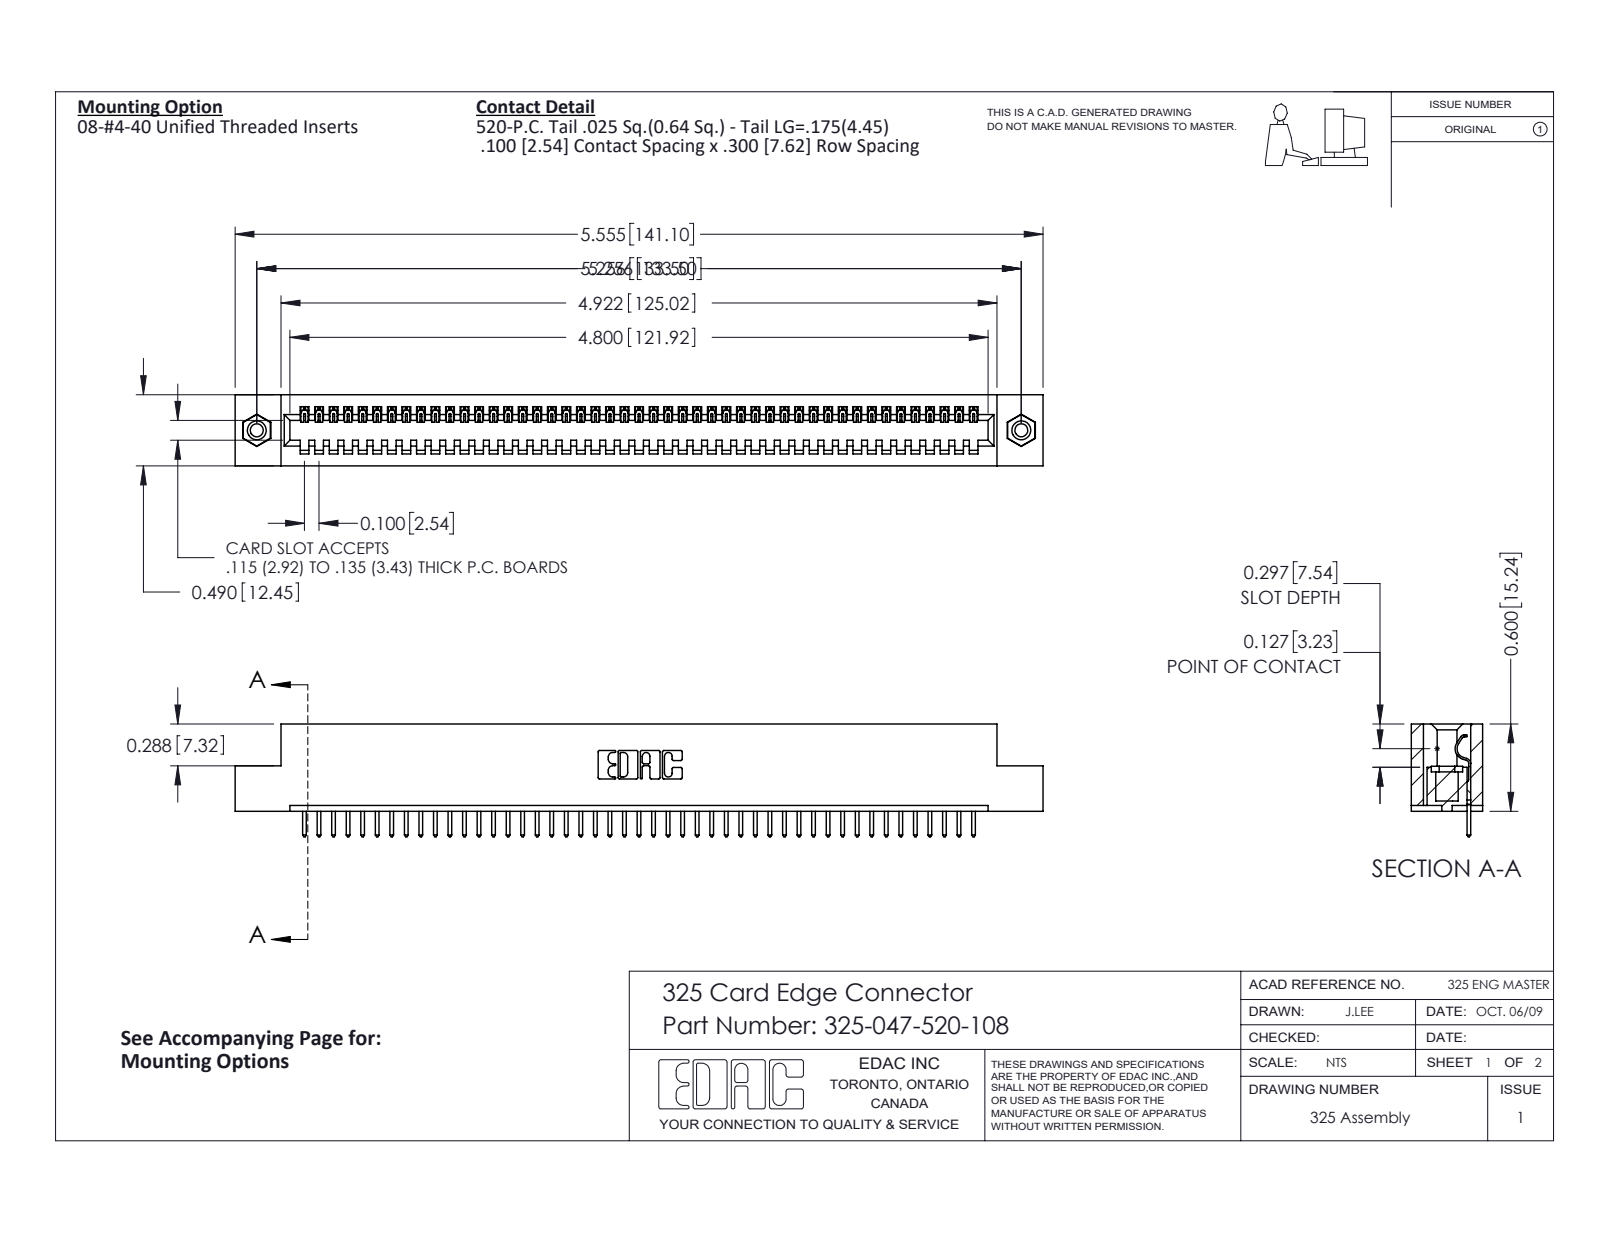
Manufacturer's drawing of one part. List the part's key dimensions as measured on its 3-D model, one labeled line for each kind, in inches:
Part name (STEP PRODUCT): 345-250-001_345-250-003-102; 325-292-001_325-293-120; 325 Part_TI; 325-047-520-108
STEP written by: SolidWorks 2016 (CONFIG_CONTROL_DESIGN)
Units: inches
Bodies: 50 solids, 2900 faces (2076 planar, 808 cylindrical, 16 other)
Overall size (bounding box): 5.555 × 0.775 × 0.49
Volume: 1.088 in³ · Surface area: 29.57 in²
Round holes (diameter × count): ⌀0.089 ×2, ⌀0.125 ×2, ⌀0.16 ×2
Round bosses / shafts (diameter × count): ⌀0.155 ×2
Partial cylindrical surfaces — rounded edges, fillets, slot ends (radius × count): R0.006 ×94, R0.01 ×94, R0.01 ×22, R0.007 ×6, R0.031 ×6, R0.026 ×3, R0.014 ×1, R0.022 ×1
Main face-to-face distances: 0.083, 0.407, 0.49, 0.3, 0.107, 0.383, 0.025, 0.325, 0.56, 0.263
Hole centre spacings: 5.256
